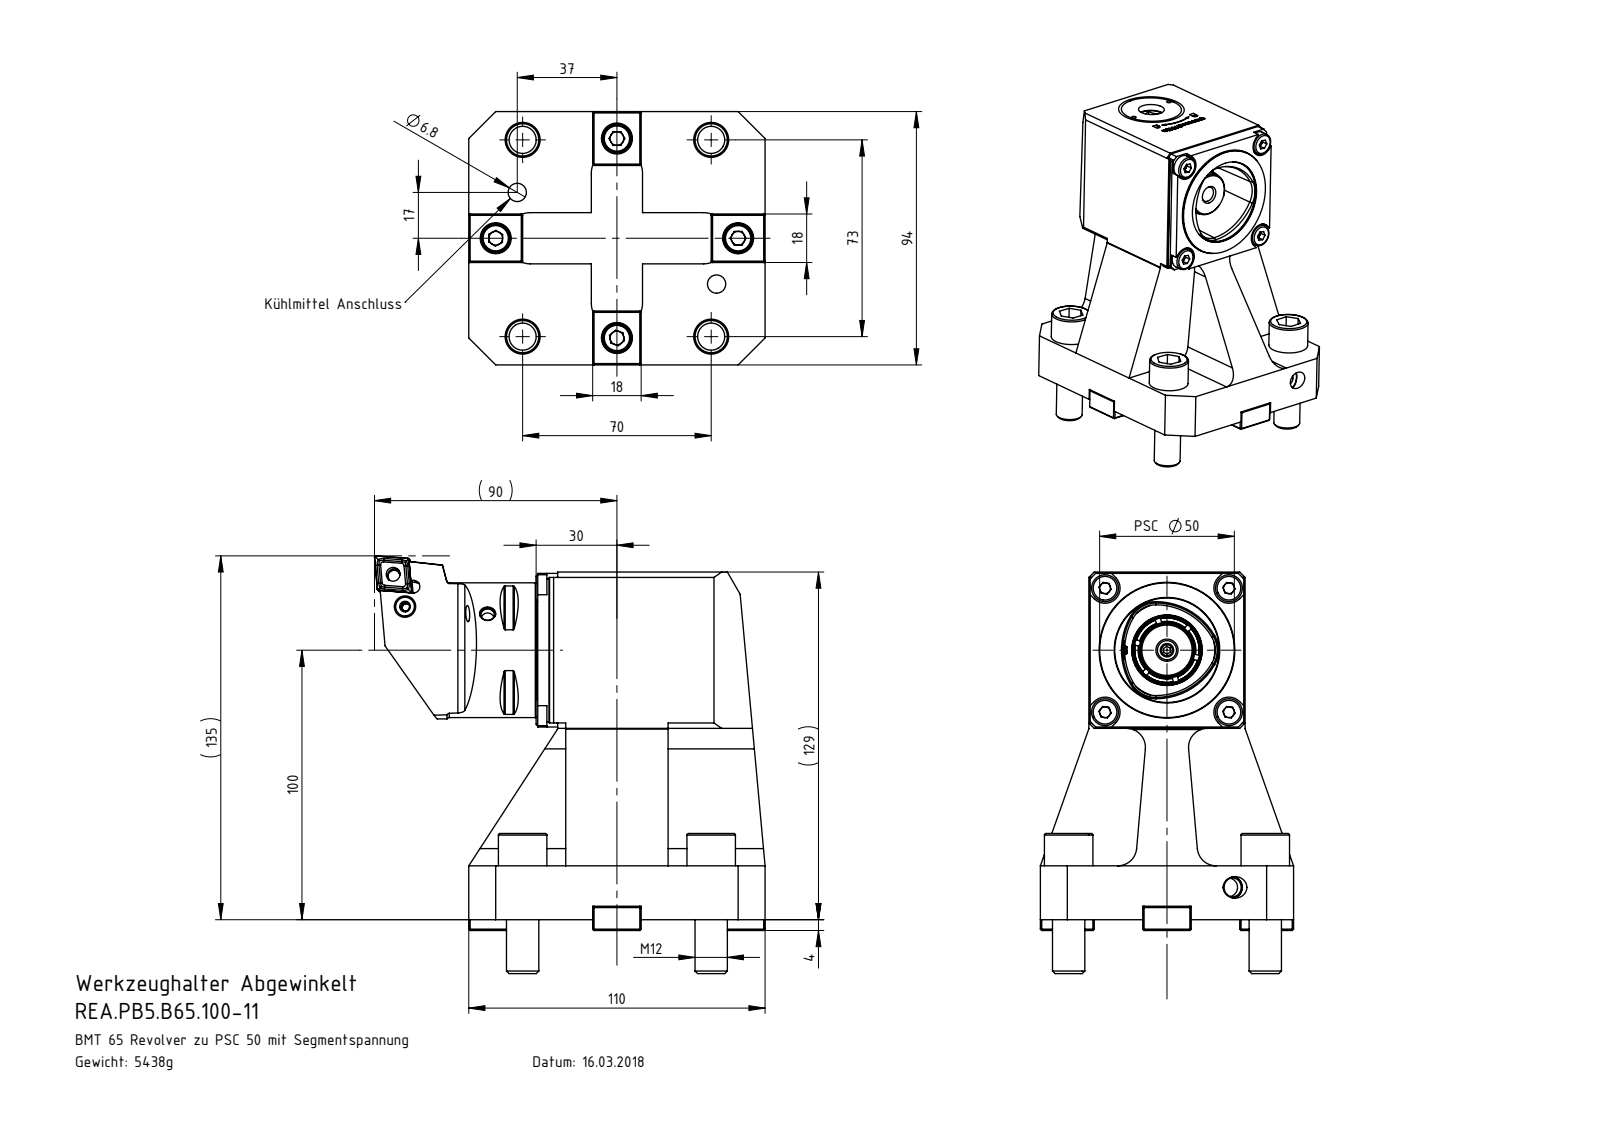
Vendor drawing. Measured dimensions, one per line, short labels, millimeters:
name: 763.18513.001.1; B65-ER1.018.009_A; DIN 3771 - 48x1.5_vorgespannt; REA.PB5.B65.100-11 (+8 more)
written by: SolidWorks 2017 (AUTOMOTIVE_DESIGN)
unit: mm
bodies: 45 solids, 1232 faces (620 planar, 249 cylindrical, 363 other)
size: 149 × 110 × 94
volume: 622 790 mm³; area: 152 486 mm²
holes: 8× ⌀5, 4× ⌀4.2, 4× ⌀6.2, 4× ⌀6.5, 4× ⌀6.8, 4× ⌀11, 4× ⌀13, 3× ⌀2.1, 3× ⌀3, 3× ⌀7, 2× ⌀3.3, 2× ⌀4.17
bosses: 8× ⌀10, 8× ⌀6, 4× ⌀18, 4× ⌀12, 2× ⌀8, 2× ⌀7, 2× ⌀4, 1× ⌀50
rounds: 10× R0.3, 8× R8, 4× R5, 4× R5.6, 4× R7, 3× R0.8, 2× R0.2, 2× R4
face distances: 20, 38, 18, 15, 5, 58, 21, 36, 76, 57
hole spacings: 32.53, 35, 37.85, 46, 58.26, 81.41, 87.93, 12.5
